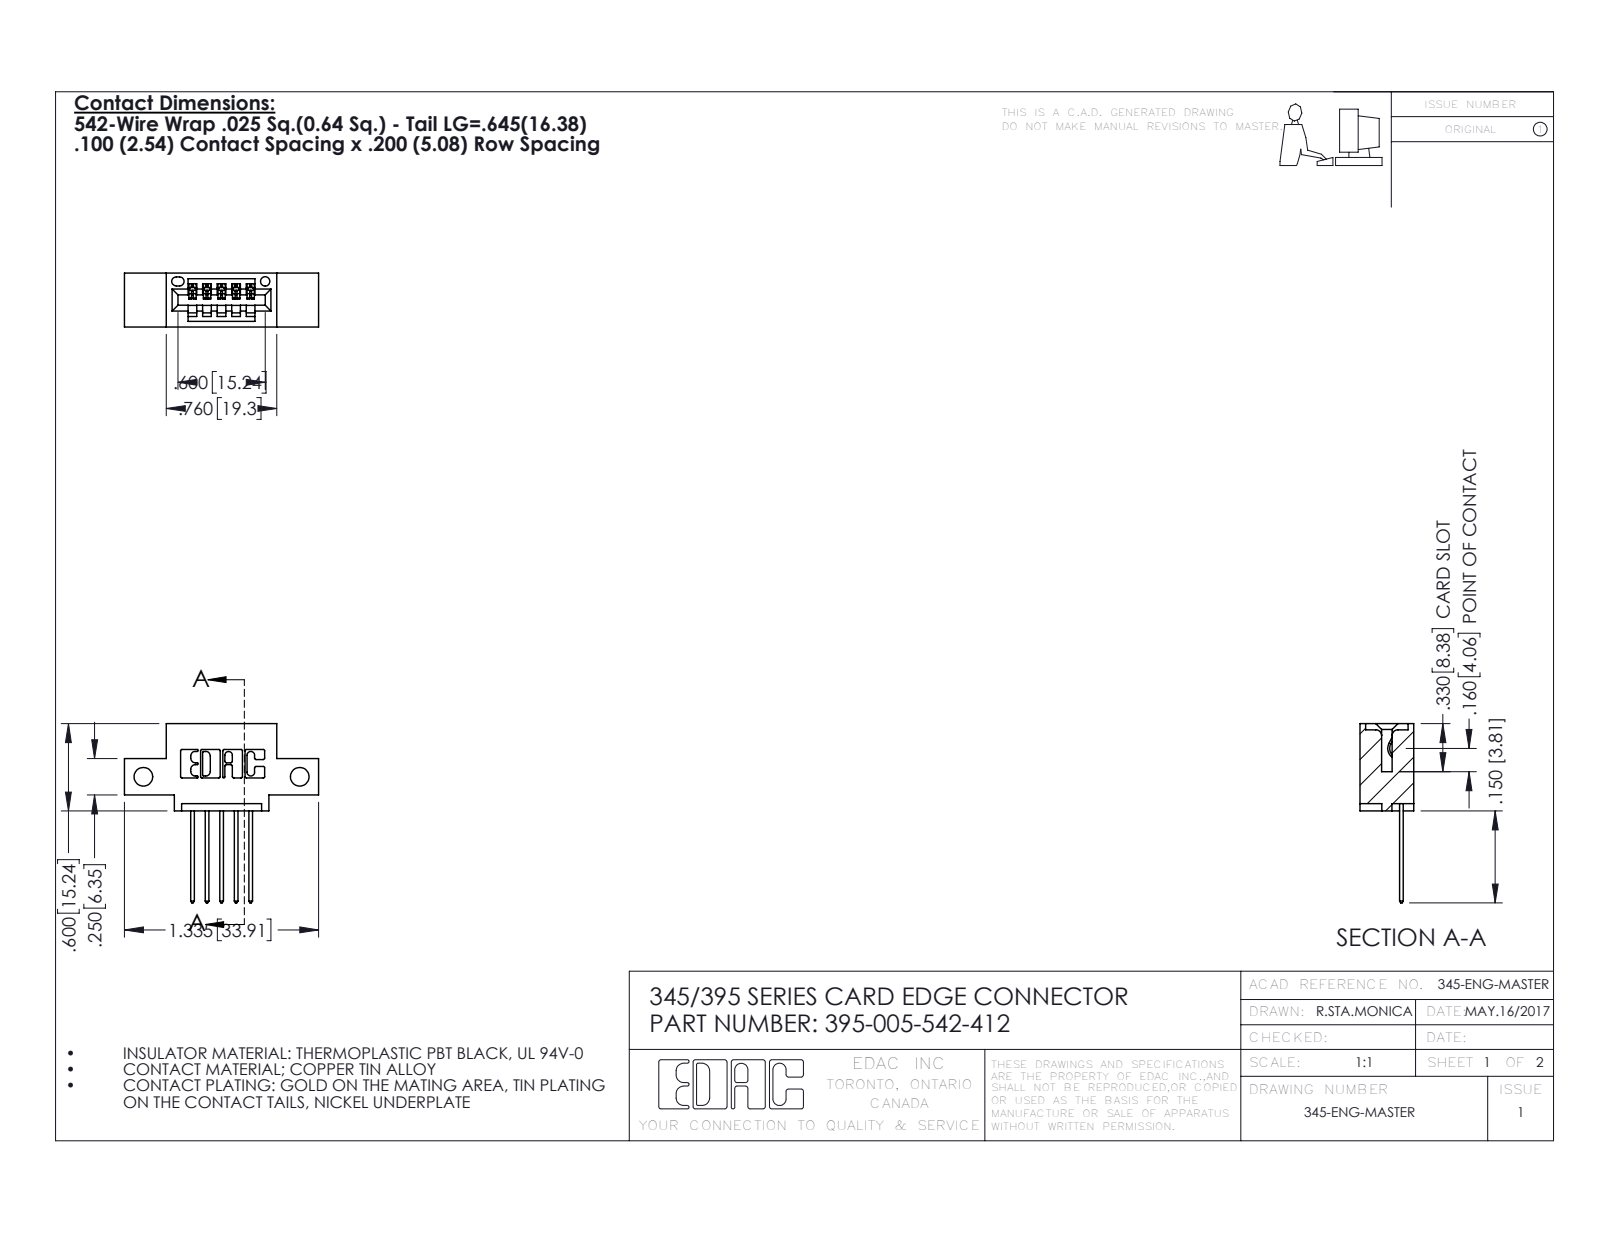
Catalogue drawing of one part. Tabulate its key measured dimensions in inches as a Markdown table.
| quantity | value |
| --- | --- |
| part name | 395-005-542-412; 345 Part_0.110 Offset - Side Mount; 345-292-001_345-293-142 |
| STEP written by | SolidWorks 2016 (CONFIG_CONTROL_DESIGN) |
| units | inches |
| bodies | 6 solids, 420 faces (284 planar, 136 cylindrical, 0 other) |
| overall size | 1.335 × 1.232 × 0.37 |
| volume | 0.169 in³ |
| surface area | 4.938 in² |
| round holes (diameter × count) | 0.128 × 2, 0.064 × 1 |
| partial cylindrical surfaces (radius × count) | 0.01 × 22, 0.006 × 10, 0.01 × 10, 0.007 × 6, 0.031 × 6, 0.026 × 3, 0.031 × 2, 0.04 × 2 |
| main face-to-face distances | 0.2, 0.37, 0.298, 0.072, 0.1, 0.025, 0.25, 0.098, 0.272, 0.06 |
| hole center spacings | 1.075 |
